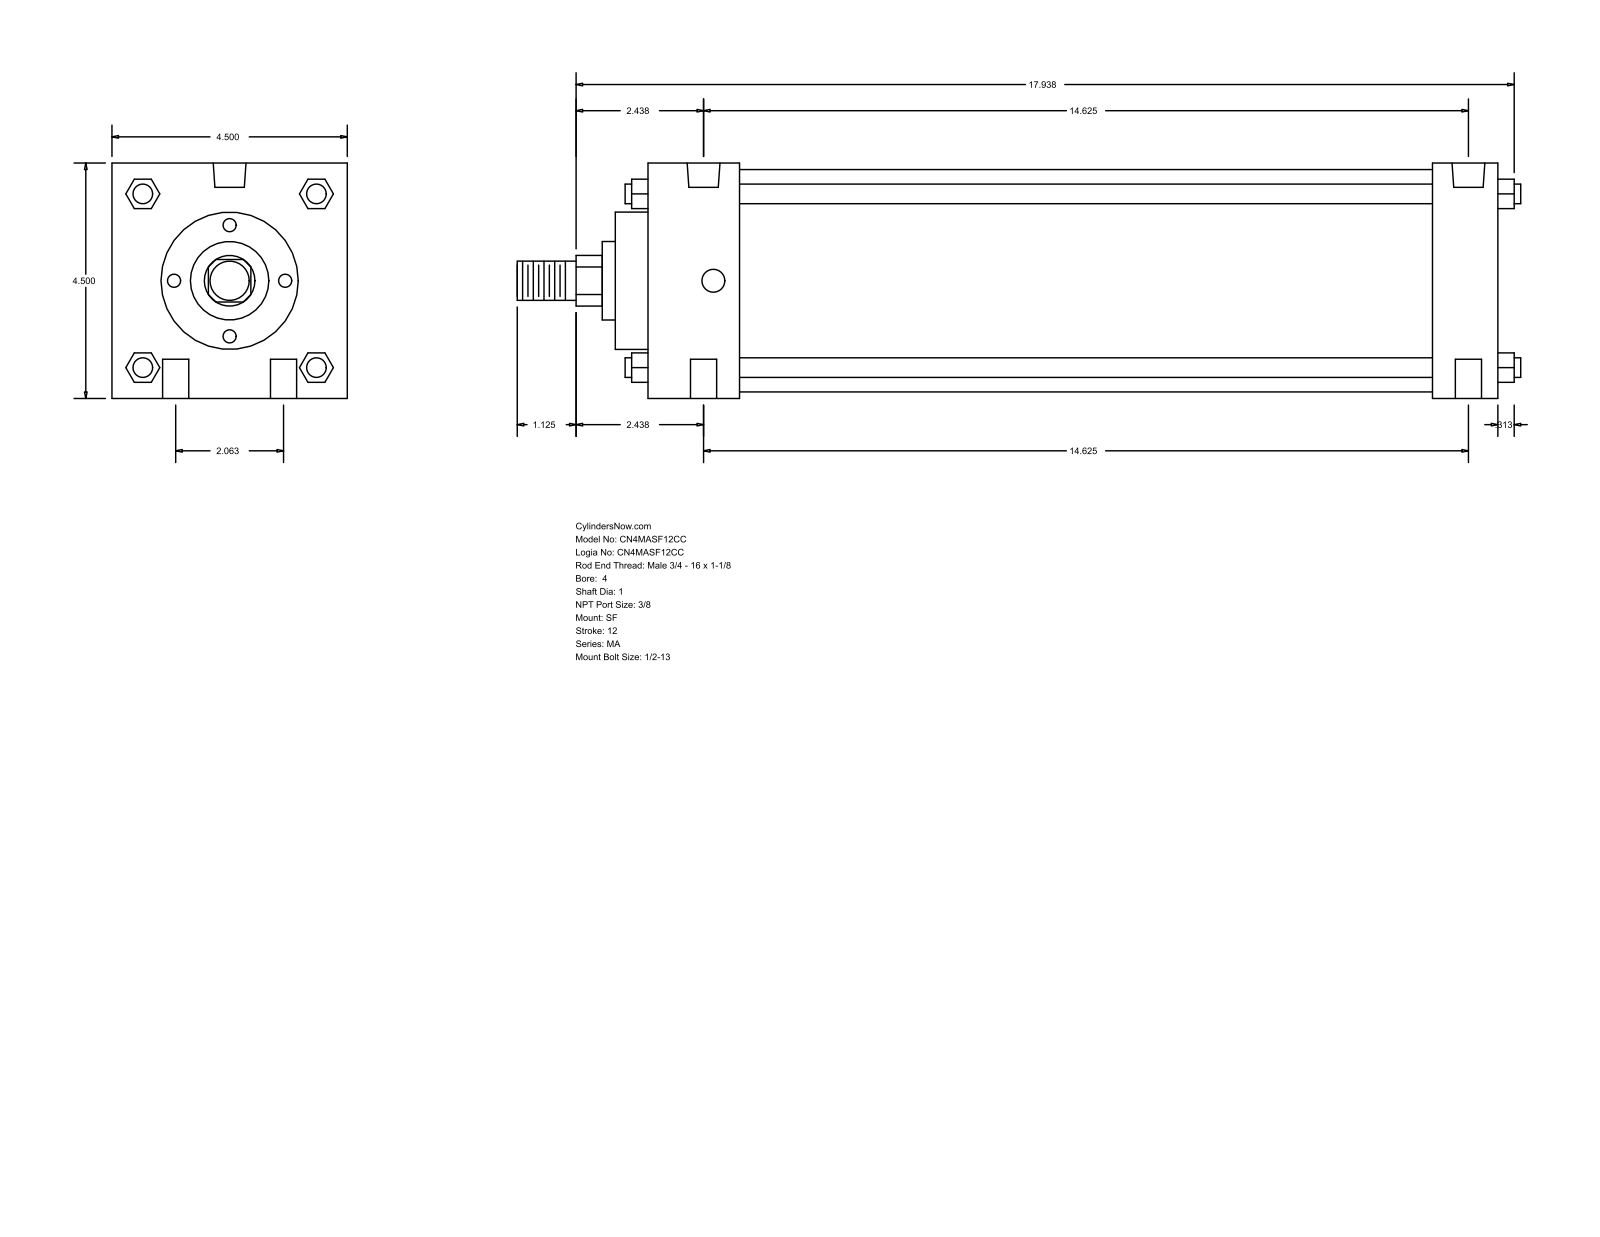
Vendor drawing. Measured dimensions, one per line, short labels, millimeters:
name: MA_SF__0400_1
written by: GSSL Pune (CONFIG_CONTROL_DESIGN)
unit: mm
bodies: 0 solids, 126 faces (95 planar, 31 cylindrical, 0 other)
size: 487.36 × 114.3 × 114.3
holes: 4× ⌀12.7, 2× ⌀11.11, 2× ⌀15.93
bosses: 4× ⌀9.53, 1× ⌀107.95, 1× ⌀66.67, 1× ⌀38.1, 1× ⌀25.4, 1× ⌀19.05
rounds: 1× R12.29
face distances: 114.3, 412.76, 381.01, 31.75, 44.46, 336.55, 368.3, 15.87, 60.33, 396.88
hole spacings: 26.19, 372.4, 371.48, 52.38, 375.15, 361.95
